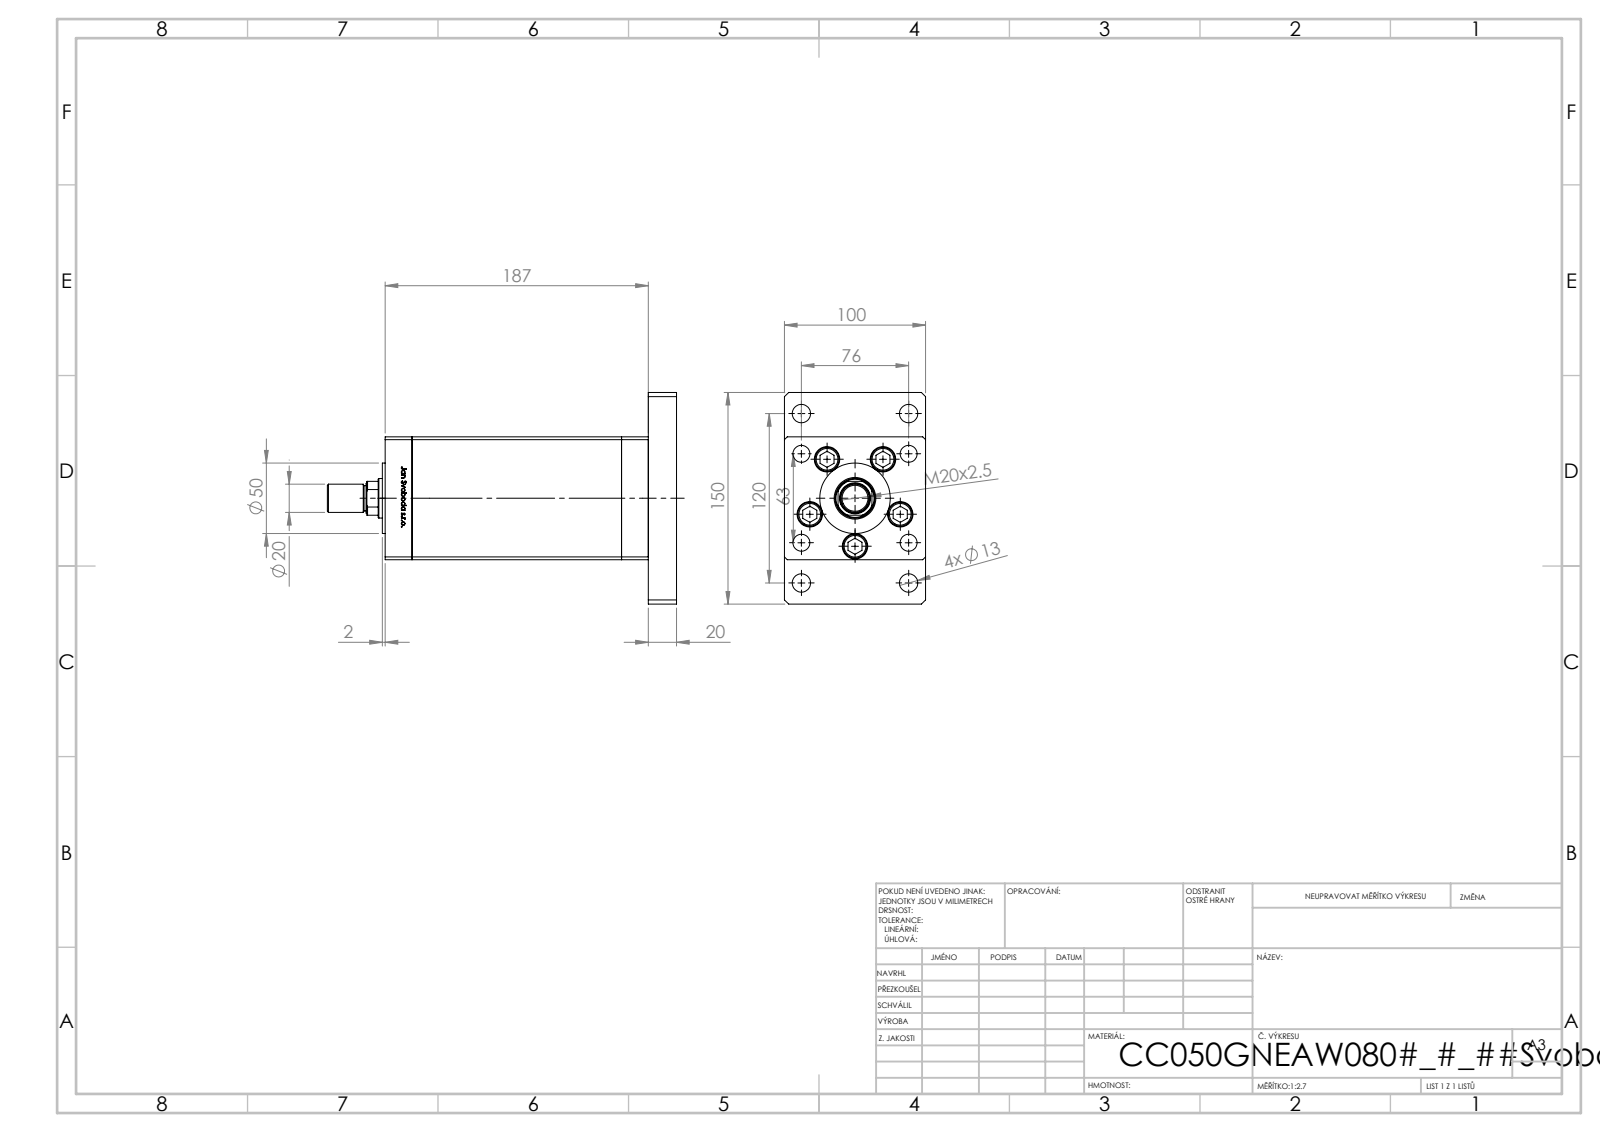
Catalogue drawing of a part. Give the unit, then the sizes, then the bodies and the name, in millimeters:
Units: millimetres
Overall size (bounding box): 247.5 × 150 × 100
Round holes (diameter × count): ⌀12 ×9, ⌀13.5 ×5, ⌀18 ×5, ⌀13 ×4, ⌀17 ×4, ⌀2 ×2, ⌀13.16 ×2, ⌀18.5 ×1, ⌀28 ×1, ⌀29.5 ×1, ⌀68 ×1
Round bosses / shafts (diameter × count): ⌀8 ×9, ⌀17 ×5, ⌀50 ×1, ⌀20 ×1, ⌀18 ×1
Partial cylindrical surfaces — rounded edges, fillets, slot ends (radius × count): R0.93 ×2, R13.5 ×1
Main face-to-face distances: 19, 100, 167.5, 87, 148.5, 20, 187.5, 39, 206.5, 186.5
Hole centre spacings: 34, 28.5, 49.36, 71.02, 76, 81.17, 91.5, 118.95
Volume: 1 706 000 mm³ · Surface area: 259 133 mm²
Bodies: 20 solids, 1324 faces (521 planar, 191 cylindrical, 612 other)
Part name (STEP PRODUCT): V220CC_MALE_METRIC; V220C_FRONT_G; V220C_F; ALLEN BOLT (+3 more)
STEP written by: SolidWorks 2019 (CONFIG_CONTROL_DESIGN)
